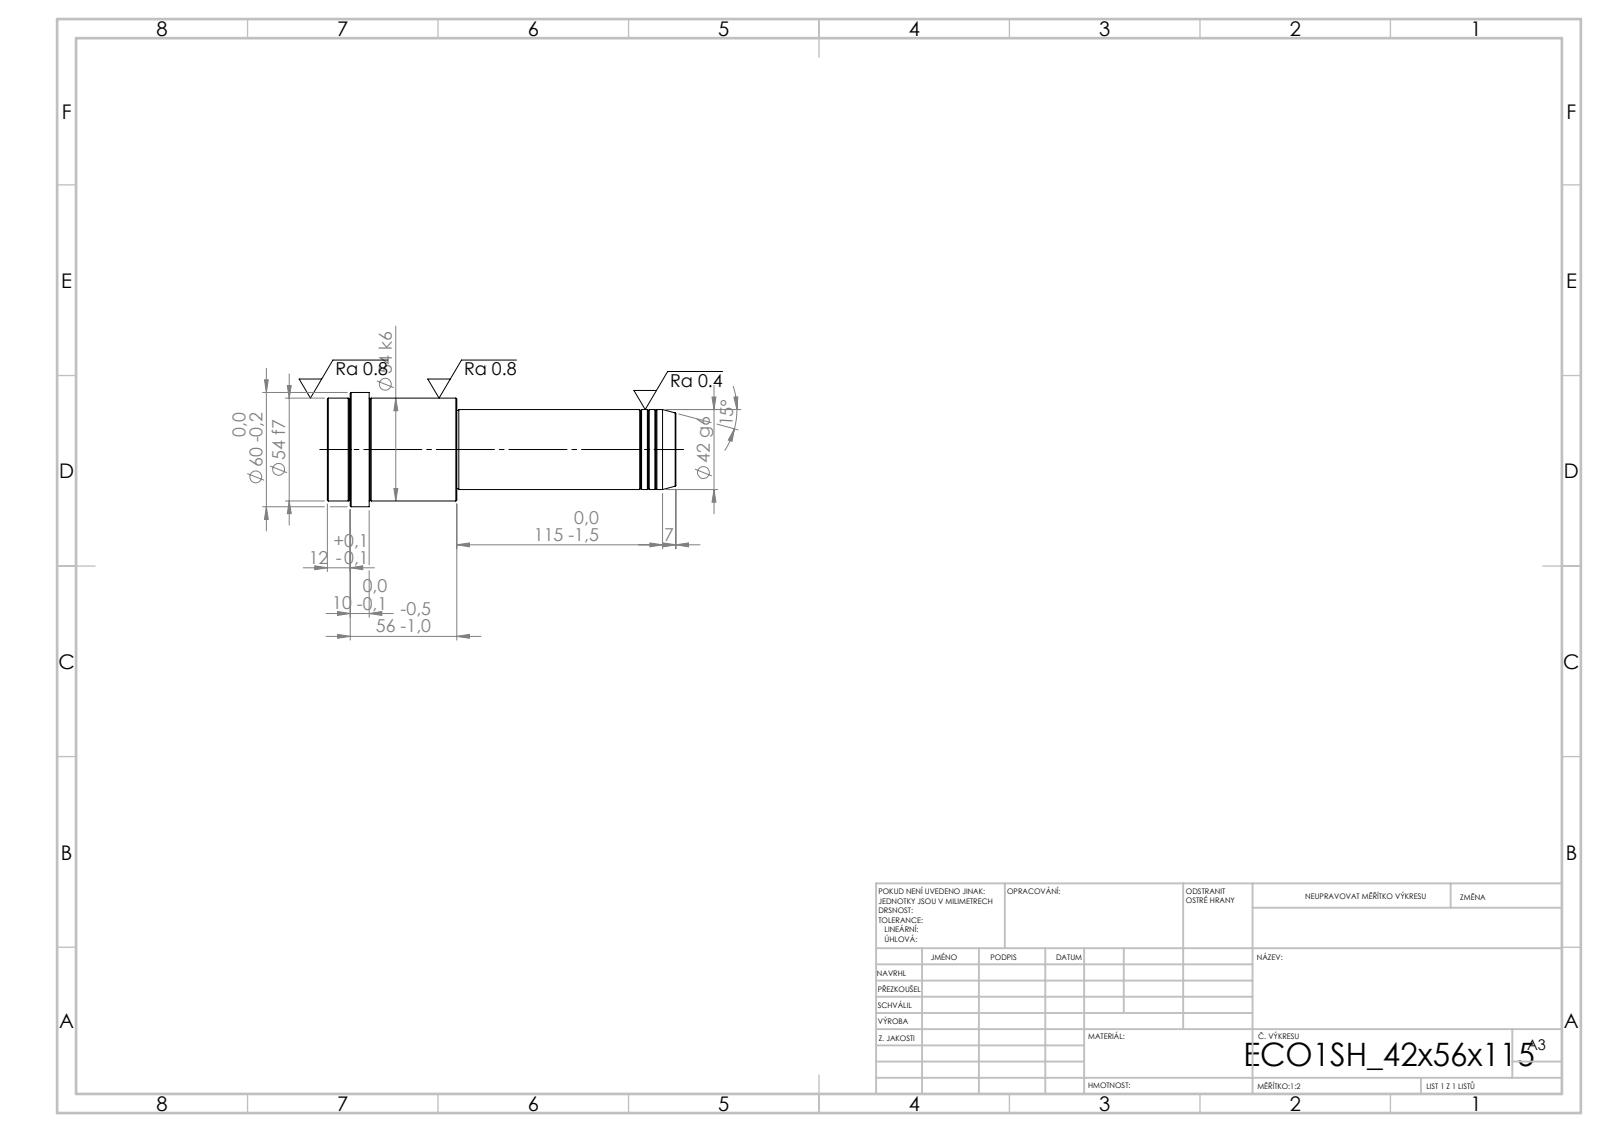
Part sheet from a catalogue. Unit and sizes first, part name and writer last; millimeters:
Units: millimetres
Overall size (bounding box): 183 × 60 × 60
Round bosses / shafts (diameter × count): ⌀60 ×1, ⌀54 ×1, ⌀42 ×1, ⌀41 ×1
Main face-to-face distances: 183, 115, 68, 161, 46, 22, 171, 56, 10, 12
Volume: 319 172 mm³ · Surface area: 32 669 mm²
Bodies: 1 solid, 52 faces (6 planar, 16 cylindrical, 30 other)
STEP written by: SolidWorks 2019 (CONFIG_CONTROL_DESIGN)
